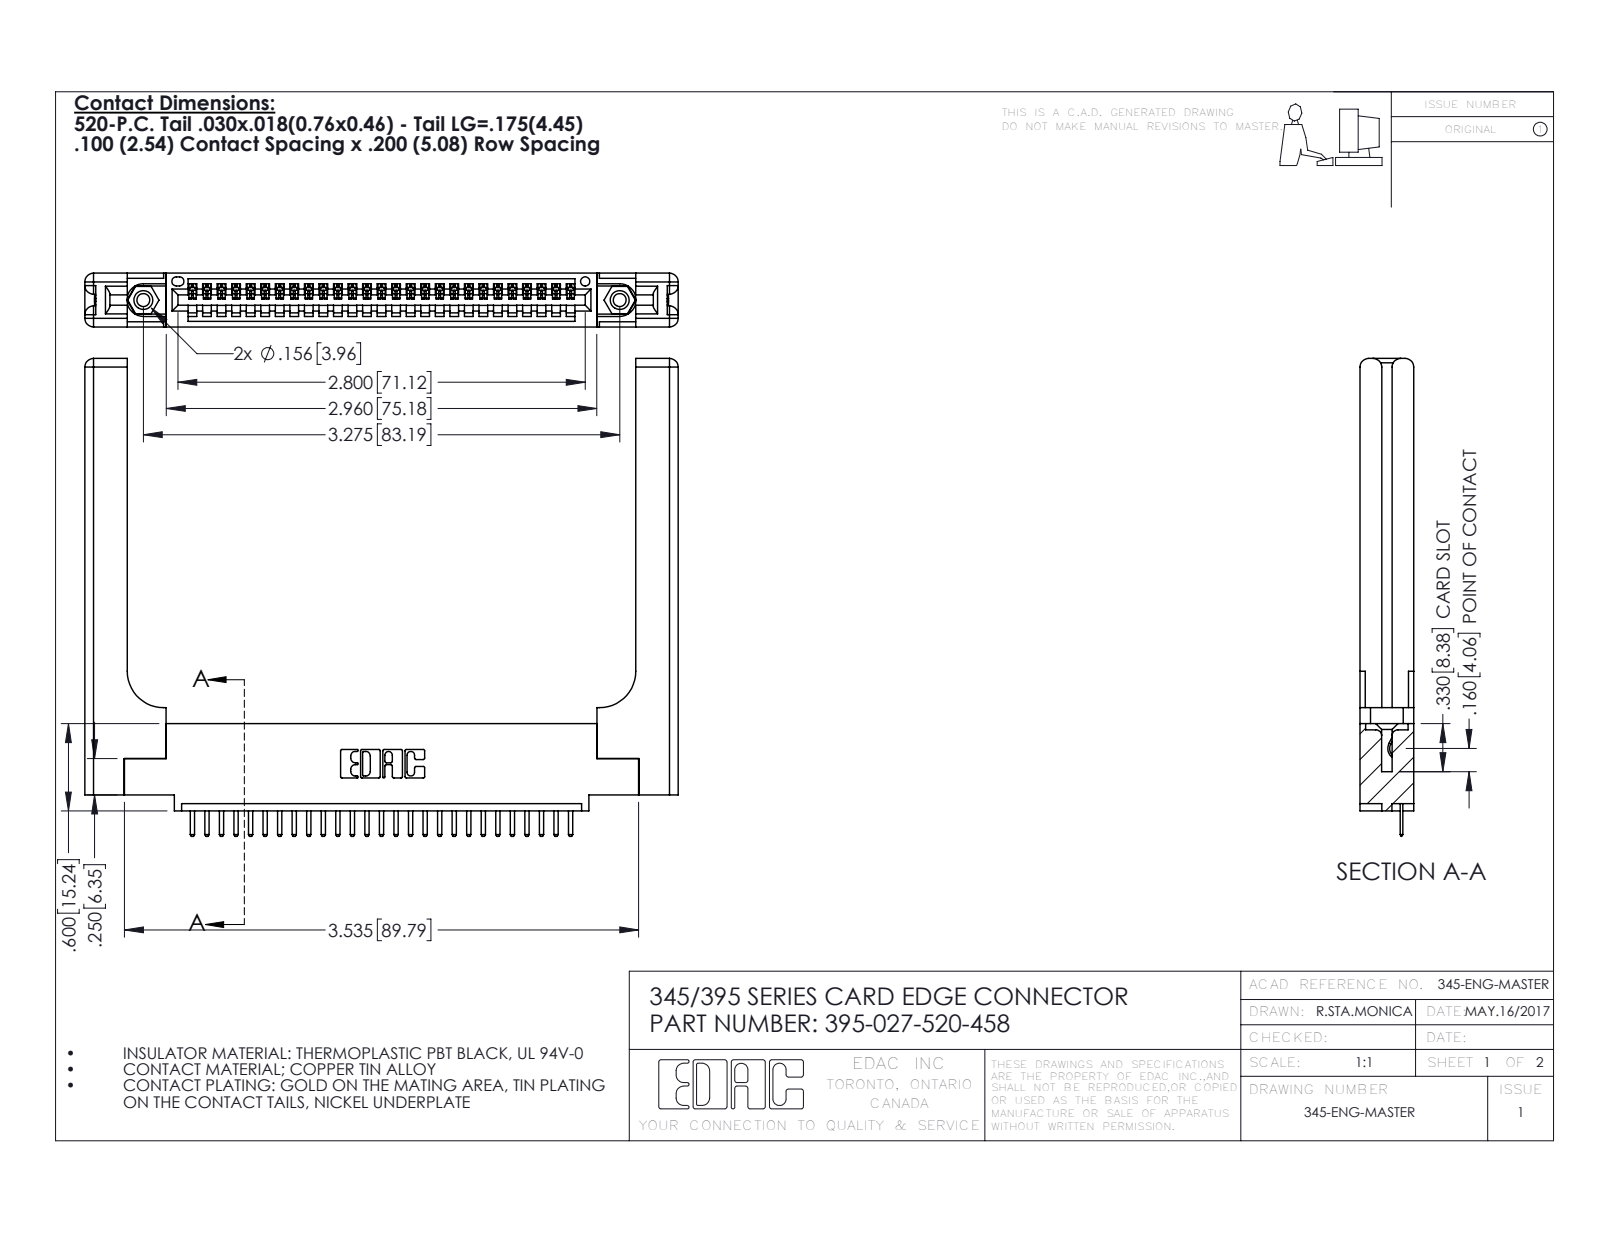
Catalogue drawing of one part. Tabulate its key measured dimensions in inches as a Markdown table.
| quantity | value |
| --- | --- |
| part name | 345-220-058_345-220-058; 345-250-001_345-250-001-102; 345-292-001_345-293-120; 345 Part_0.110 Offset - 0.156 Dia-TH (+1 more) |
| STEP written by | SolidWorks 2016 (CONFIG_CONTROL_DESIGN) |
| units | inches |
| bodies | 32 solids, 2060 faces (1366 planar, 634 cylindrical, 60 other) |
| overall size | 4.079 × 3.285 × 0.37 |
| volume | 1.103 in³ |
| surface area | 27.35 in² |
| round holes (diameter × count) | 0.089 × 2, 0.125 × 2, 0.156 × 2, 0.064 × 1 |
| round bosses / shafts (diameter × count) | 0.155 × 2 |
| partial cylindrical surfaces (radius × count) | 0.01 × 56, 0.006 × 54, 0.01 × 22, 0.06 × 16, 0.007 × 6, 0.031 × 6, 0.026 × 3, 0.03 × 2 |
| main face-to-face distances | 0.37, 0.072, 0.298, 0.148, 0.15, 0.077, 0.22, 0.098, 0.272, 0.025 |
| hole center spacings | 0.27, 3.04, 3.275 |
